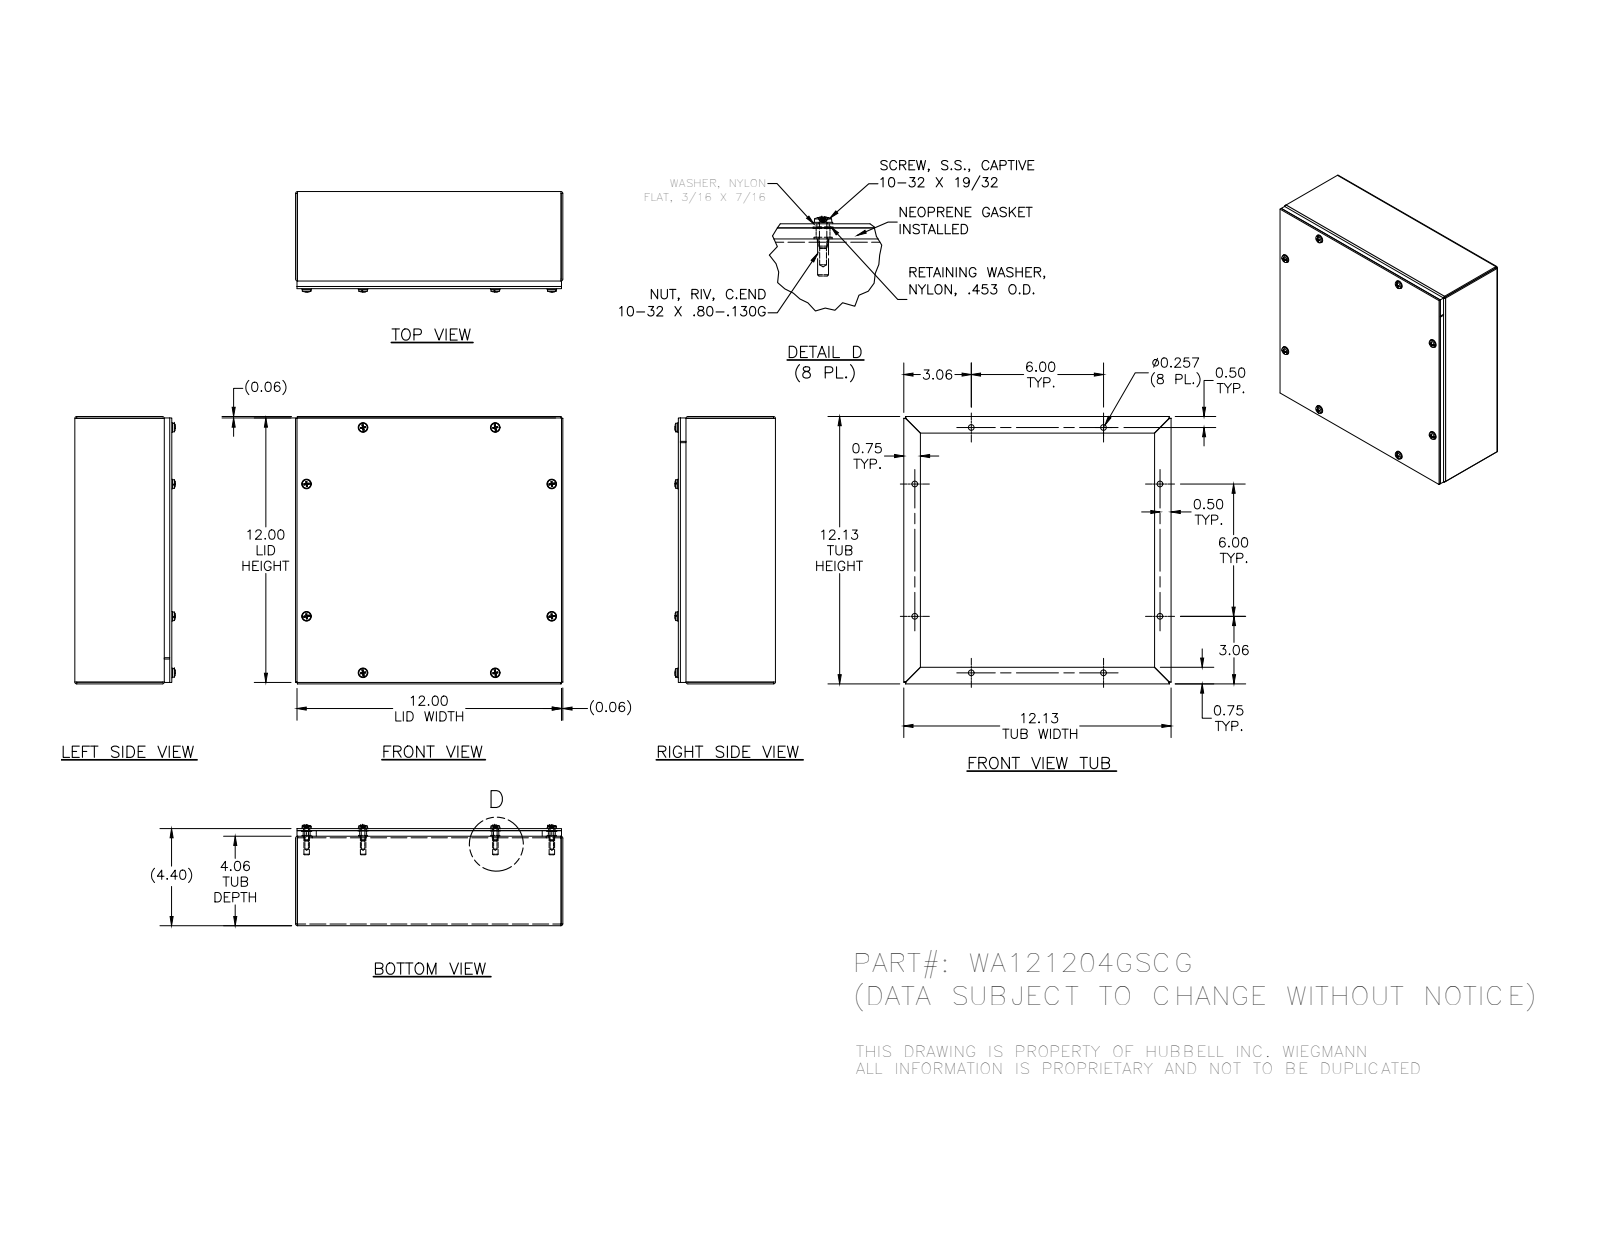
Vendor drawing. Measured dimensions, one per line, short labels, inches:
name: 39035; 39077; 37210; 34984 (+4 more)
written by: SolidWorks 2014 (AUTOMOTIVE_DESIGN)
unit: in
bodies: 36 solids, 892 faces (420 planar, 240 cylindrical, 232 other)
size: 12.125 × 12.125 × 4.558
volume: 50.62 in³; area: 1 153 in²
holes: 8× ⌀0.156, 8× ⌀0.188, 8× ⌀0.196, 8× ⌀0.257, 8× ⌀0.278, 8× ⌀0.281, 8× ⌀0.313
bosses: 8× ⌀0.453, 8× ⌀0.437, 8× ⌀0.406, 8× ⌀0.248, 8× ⌀0.167
rounds: 8× R0.016, 8× R0.089, 8× R0.09
face distances: 0.074, 0.094, 4.33, 4.404, 4.236, 4.31, 3.986, 0.074, 12.125, 12.051
hole spacings: 6, 8.937, 8.938, 8.937, 3.624, 12.109, 8.937, 8.938
